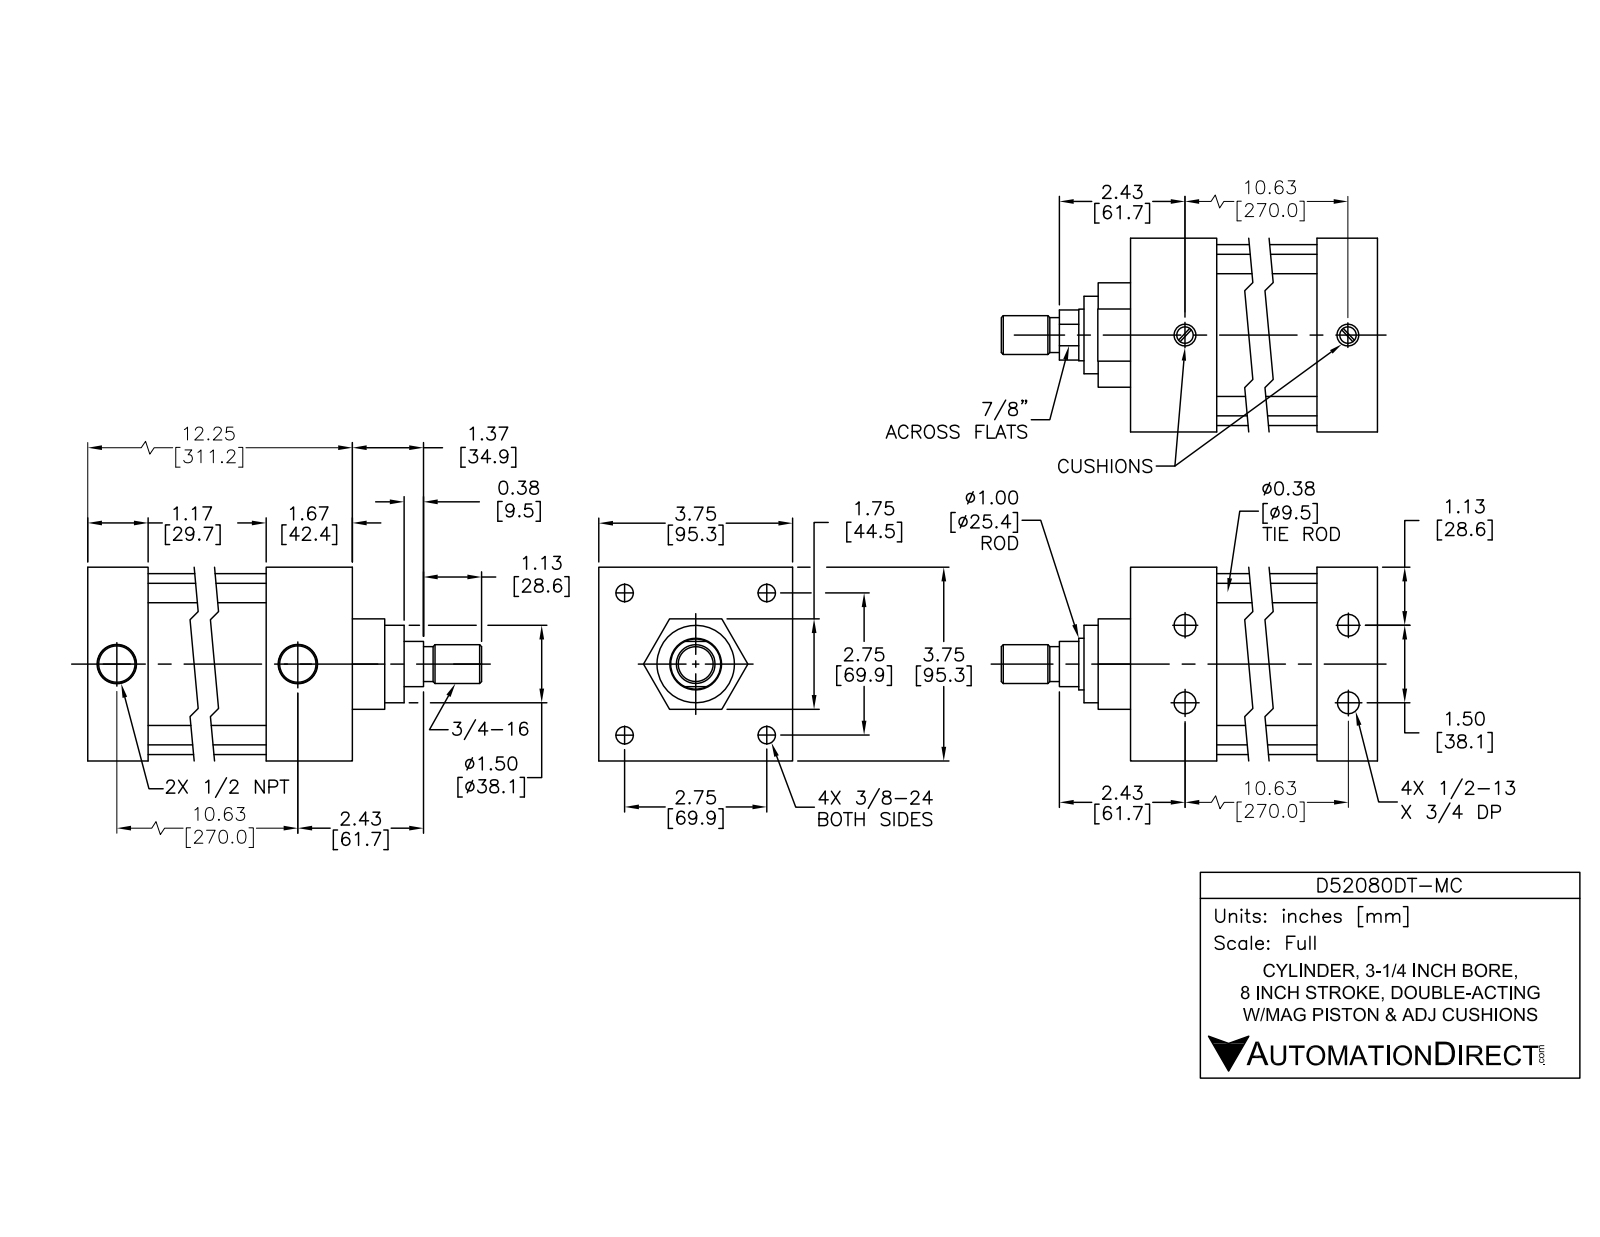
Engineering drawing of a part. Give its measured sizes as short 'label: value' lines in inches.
name: D52080DT-MC; D52080DT-M BODY; D52080DT-M PISTON
written by: SolidWorks 2015 (AUTOMOTIVE_DESIGN)
unit: in
bodies: 12 solids, 303 faces (99 planar, 114 cylindrical, 90 other)
size: 14.745 × 3.75 × 3.75
volume: 73.58 in³; area: 466 in²
holes: 4× ⌀0.33, 4× ⌀0.406, 4× ⌀0.417, 4× ⌀0.625, 2× ⌀0.5, 2× ⌀0.766, 1× ⌀1, 1× ⌀1.003, 1× ⌀3.25
bosses: 4× ⌀0.609, 4× ⌀0.375, 4× ⌀0.34, 1× ⌀3.5, 1× ⌀3.247, 1× ⌀1.75, 1× ⌀0.997, 1× ⌀0.97
rounds: 4× R0.375
face distances: 3.75, 0.08, 9.326, 12.246, 1.75, 10.997, 1.249, 9.751, 1.246, 2.495
hole spacings: 0.75, 0.76, 1.5, 1.95, 1.95, 2.758, 2.758, 3.9
